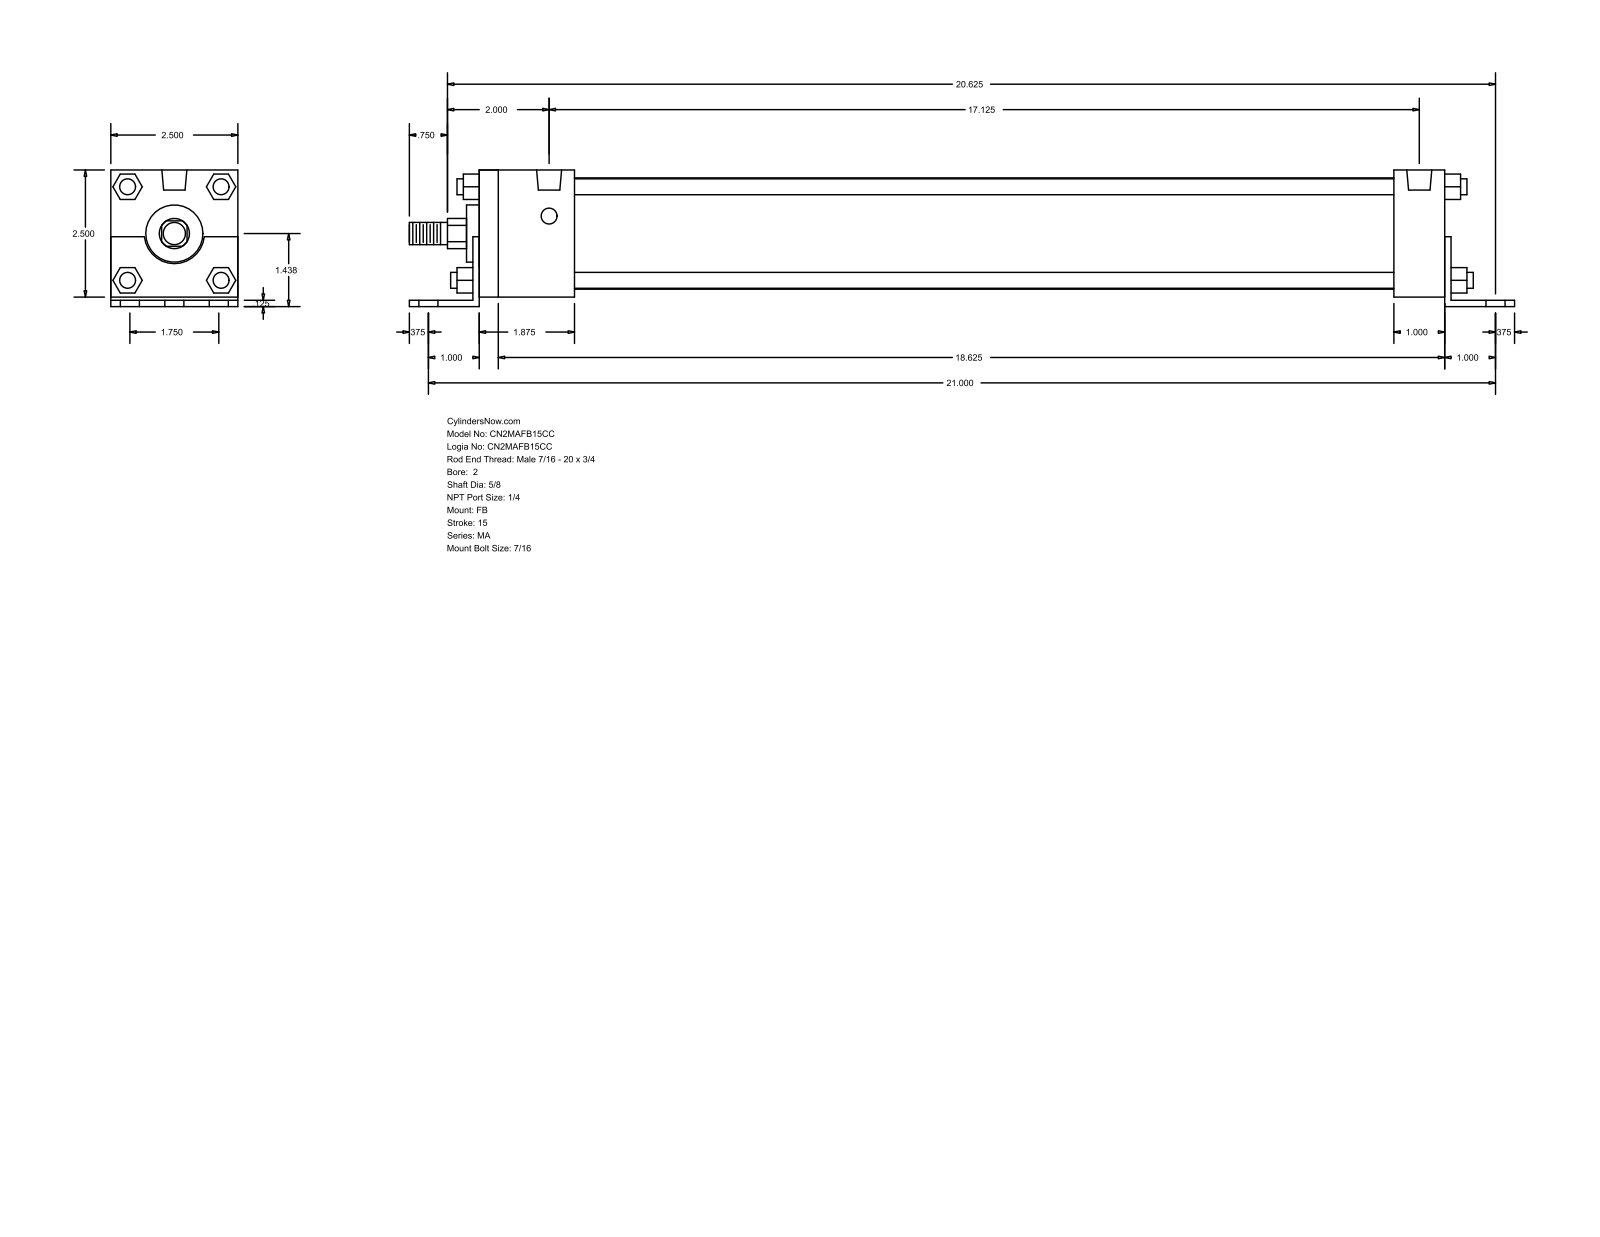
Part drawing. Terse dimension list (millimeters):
name: MA_FB__0200_0.625
written by: GSSL Pune (CONFIG_CONTROL_DESIGN)
unit: mm
bodies: 0 solids, 140 faces (105 planar, 35 cylindrical, 0 other)
size: 552.45 × 68.26 × 63.5
holes: 6× ⌀11.11, 4× ⌀7.94, 2× ⌀12.49
bosses: 4× ⌀7.94, 1× ⌀55.63, 1× ⌀28.57, 1× ⌀15.88, 1× ⌀11.11
rounds: 1× R7.54, 1× R15.05
face distances: 63.5, 3.17, 4.76, 68.26, 1.59, 65.09, 488.95, 3.18, 482.6, 485.77
hole spacings: 22.23, 533.87, 533.41, 44.12, 44.46, 64.3, 434.97, 473.6
